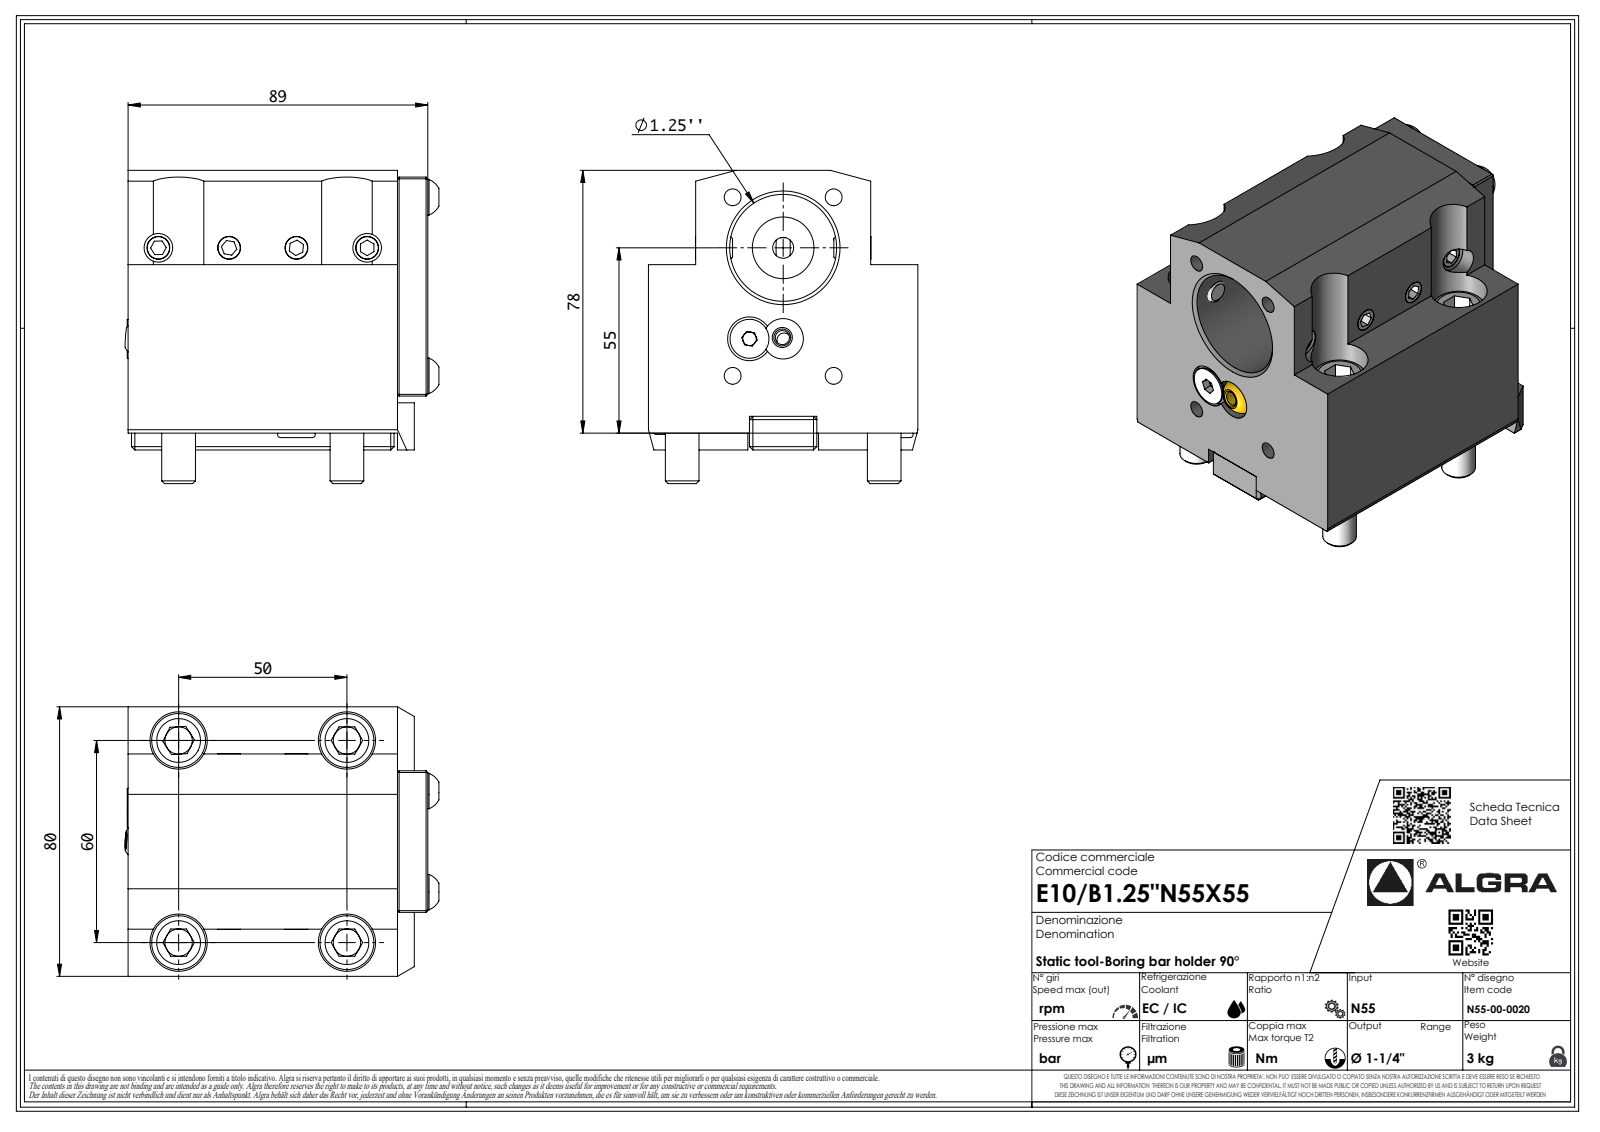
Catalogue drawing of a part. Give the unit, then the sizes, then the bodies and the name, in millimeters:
Units: millimetres
Overall size (bounding box): 93 × 89.91 × 80
Round holes (diameter × count): ⌀2.1 ×1, ⌀31.75 ×1
Round bosses / shafts (diameter × count): ⌀10 ×4, ⌀6.37 ×1, ⌀1.7 ×1
Partial cylindrical surfaces — rounded edges, fillets, slot ends (radius × count): R0.33 ×7, R0.52 ×7, R3.7 ×7, R10.5 ×2, R0.21 ×1
Main face-to-face distances: 80, 14, 66, 5, 50, 9, 89, 78, 28, 52
Volume: 410 747 mm³ · Surface area: 51 285 mm²
Bodies: 1 solid, 411 faces (298 planar, 35 cylindrical, 78 other)
Part name (STEP PRODUCT): E10B1.25N55X55
STEP written by: SolidWorks 2023 (AUTOMOTIVE_DESIGN)
